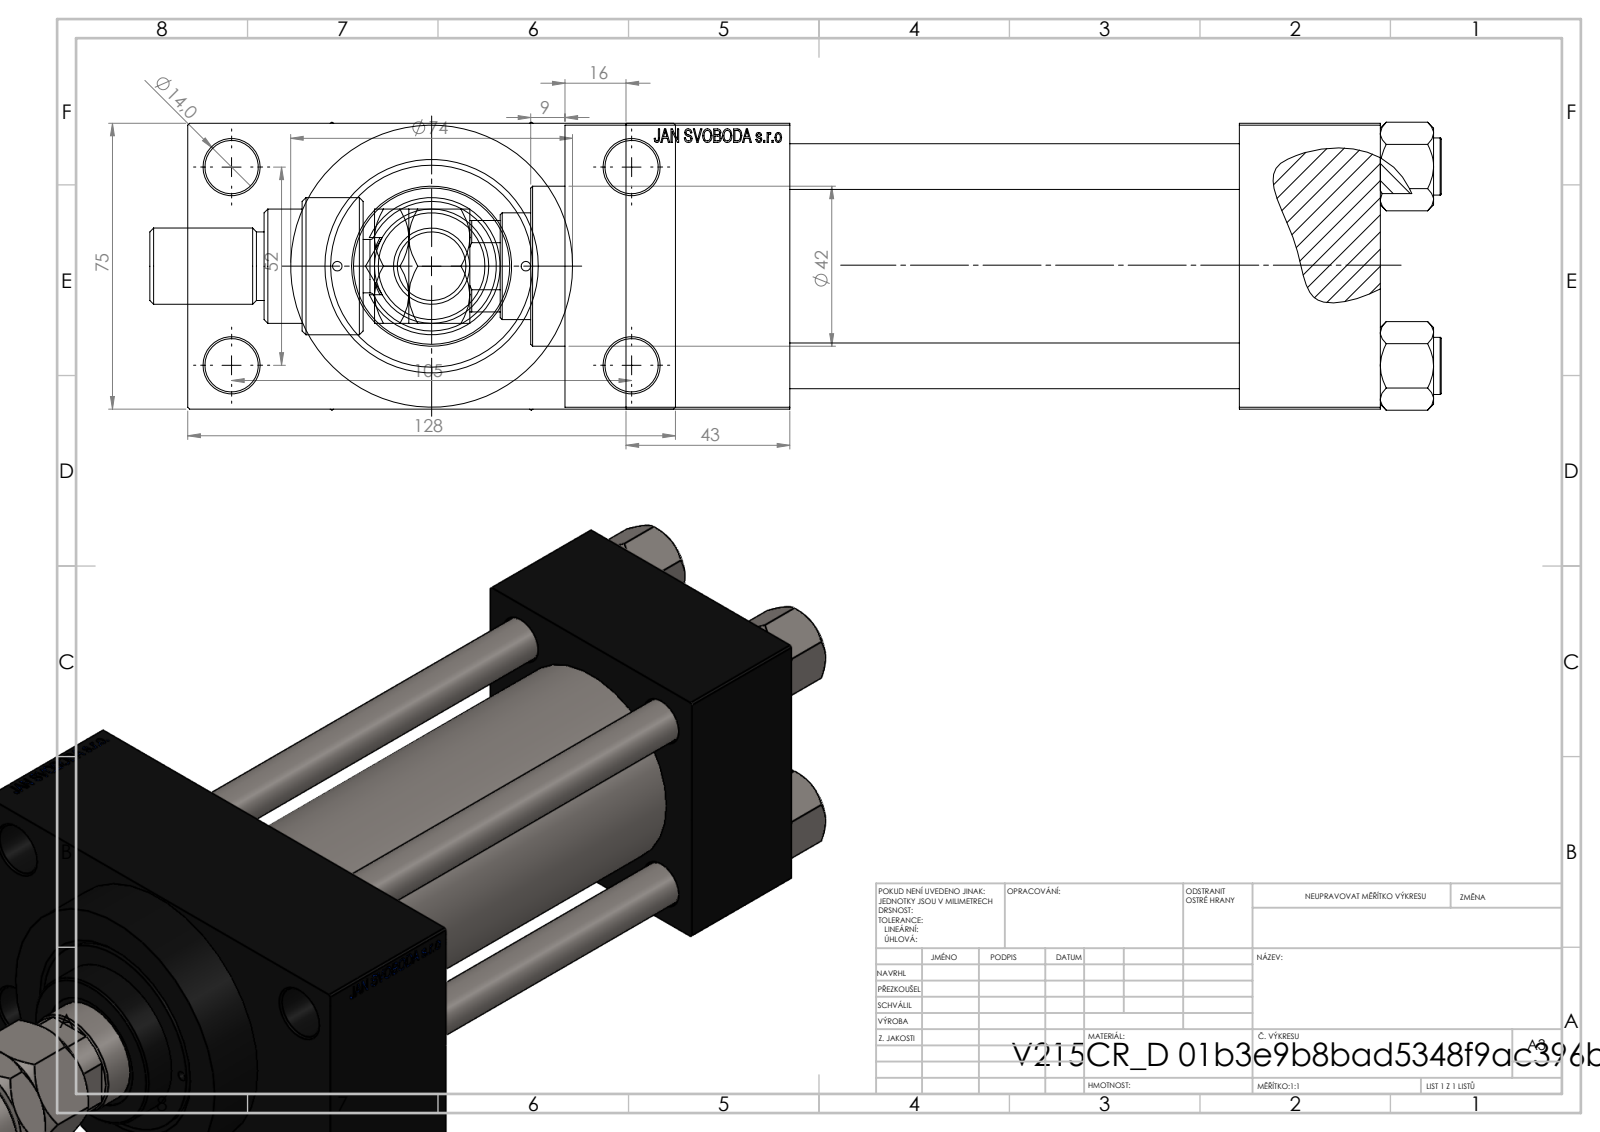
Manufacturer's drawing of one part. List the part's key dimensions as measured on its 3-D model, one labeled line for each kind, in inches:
Part name (STEP PRODUCT): MFA; NUT_M5_D; V215_VC_A; V215CR_VCP_D (+3 more)
STEP written by: SolidWorks 2019 (CONFIG_CONTROL_DESIGN)
Units: inches
Bodies: 13 solids, 1196 faces (527 planar, 105 cylindrical, 564 other)
Overall size (bounding box): 13.346 × 5.039 × 2.974
Volume: 57.91 in³ · Surface area: 338 in²
Round holes (diameter × count): ⌀0.472 ×4, ⌀0.551 ×4, ⌀0.098 ×2, ⌀0.276 ×2, ⌀0.825 ×2, ⌀1.181 ×2, ⌀0.728 ×1, ⌀1.102 ×1, ⌀1.22 ×1, ⌀1.614 ×1, ⌀1.969 ×1, ⌀2.087 ×1
Round bosses / shafts (diameter × count): ⌀0.591 ×4, ⌀2.913 ×1, ⌀2.205 ×1, ⌀1.654 ×1, ⌀1.417 ×1, ⌀1.181 ×1, ⌀0.866 ×1, ⌀0.787 ×1
Partial cylindrical surfaces — rounded edges, fillets, slot ends (radius × count): R0.295 ×1, R0.472 ×1, R0.531 ×1
Main face-to-face distances: 2.953, 4.646, 6.102, 1.457, 1.043, 1.693, 7.795, 6.339, 3.996, 0.63
Hole centre spacings: 1.031, 1.037, 1.456, 1.497, 2.059, 2.253, 2.3, 2.307
